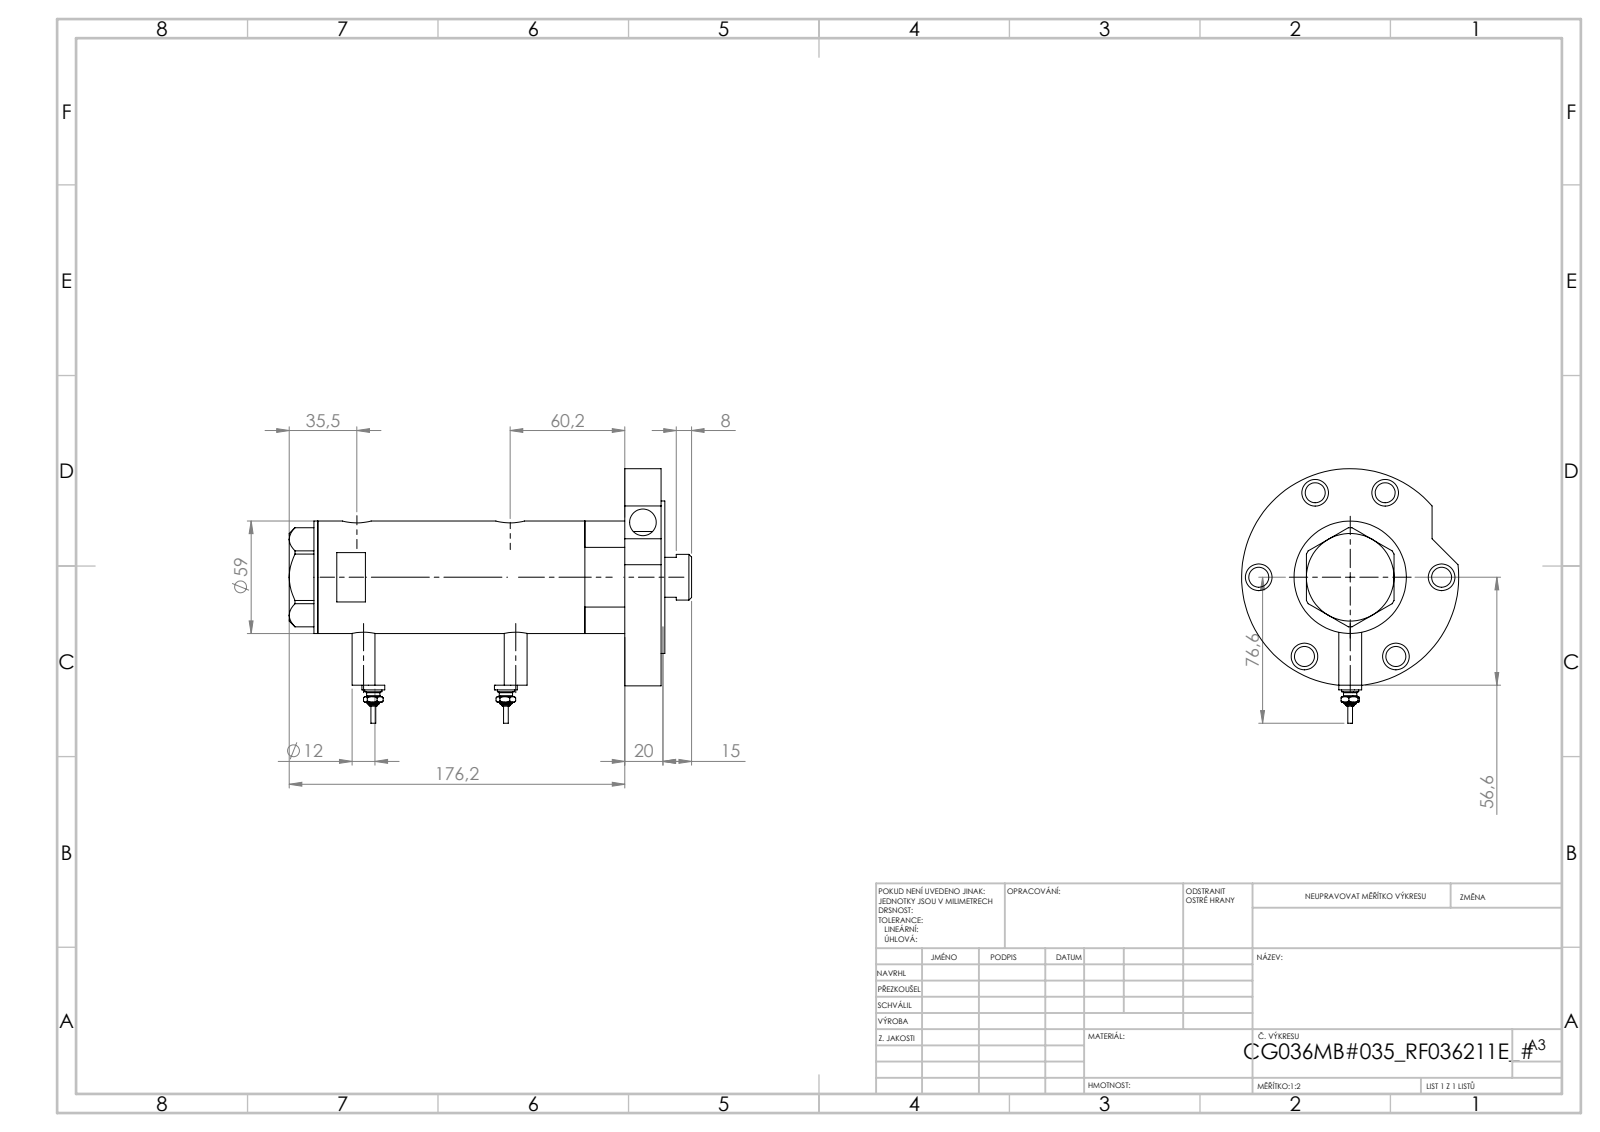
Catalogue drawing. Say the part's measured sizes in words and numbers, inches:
The part is named "V270CG_RF211E; V270CG_FRONT; V270CG_VC; V270CG_SWITCH (+2 more)". Its 3-D file was written by "SolidWorks 2019 (CONFIG_CONTROL_DESIGN)". It is 7 solids with 276 faces: 92 planar, 110 cylindrical and 74 other. Overall it measures 7.812 by 4.677 by 4.488 inches. Its volume is 35.85 cubic inches and its surface area 202.3 square inches. Round holes: 7 of diameter 0.551, 6 of diameter 0.413, 2 of diameter 0.197, 2 of diameter 0.383, 2 of diameter 0.492, 2 of diameter 0.591, 1 of diameter 0.335, 1 of diameter 0.984, 1 of diameter 1.043, 1 of diameter 1.417, 1 of diameter 1.575, 1 of diameter 1.89. Round bosses or shafts: 3 of diameter 0.472, 2 of diameter 0.354, 2 of diameter 0.276, 2 of diameter 0.171, 2 of diameter 0.094, 1 of diameter 4.488, 1 of diameter 3.15, 1 of diameter 2.323. The main face-to-face distances are 0.748, 0.079, 6.569, 0.827, 5.742, 6.49, 3.635, 2.106, 2.854, 2.933. The hole center spacings are 1.89, 0.114, 0.138, 2.1, 2.644, 2.758, 2.781, 2.896.
